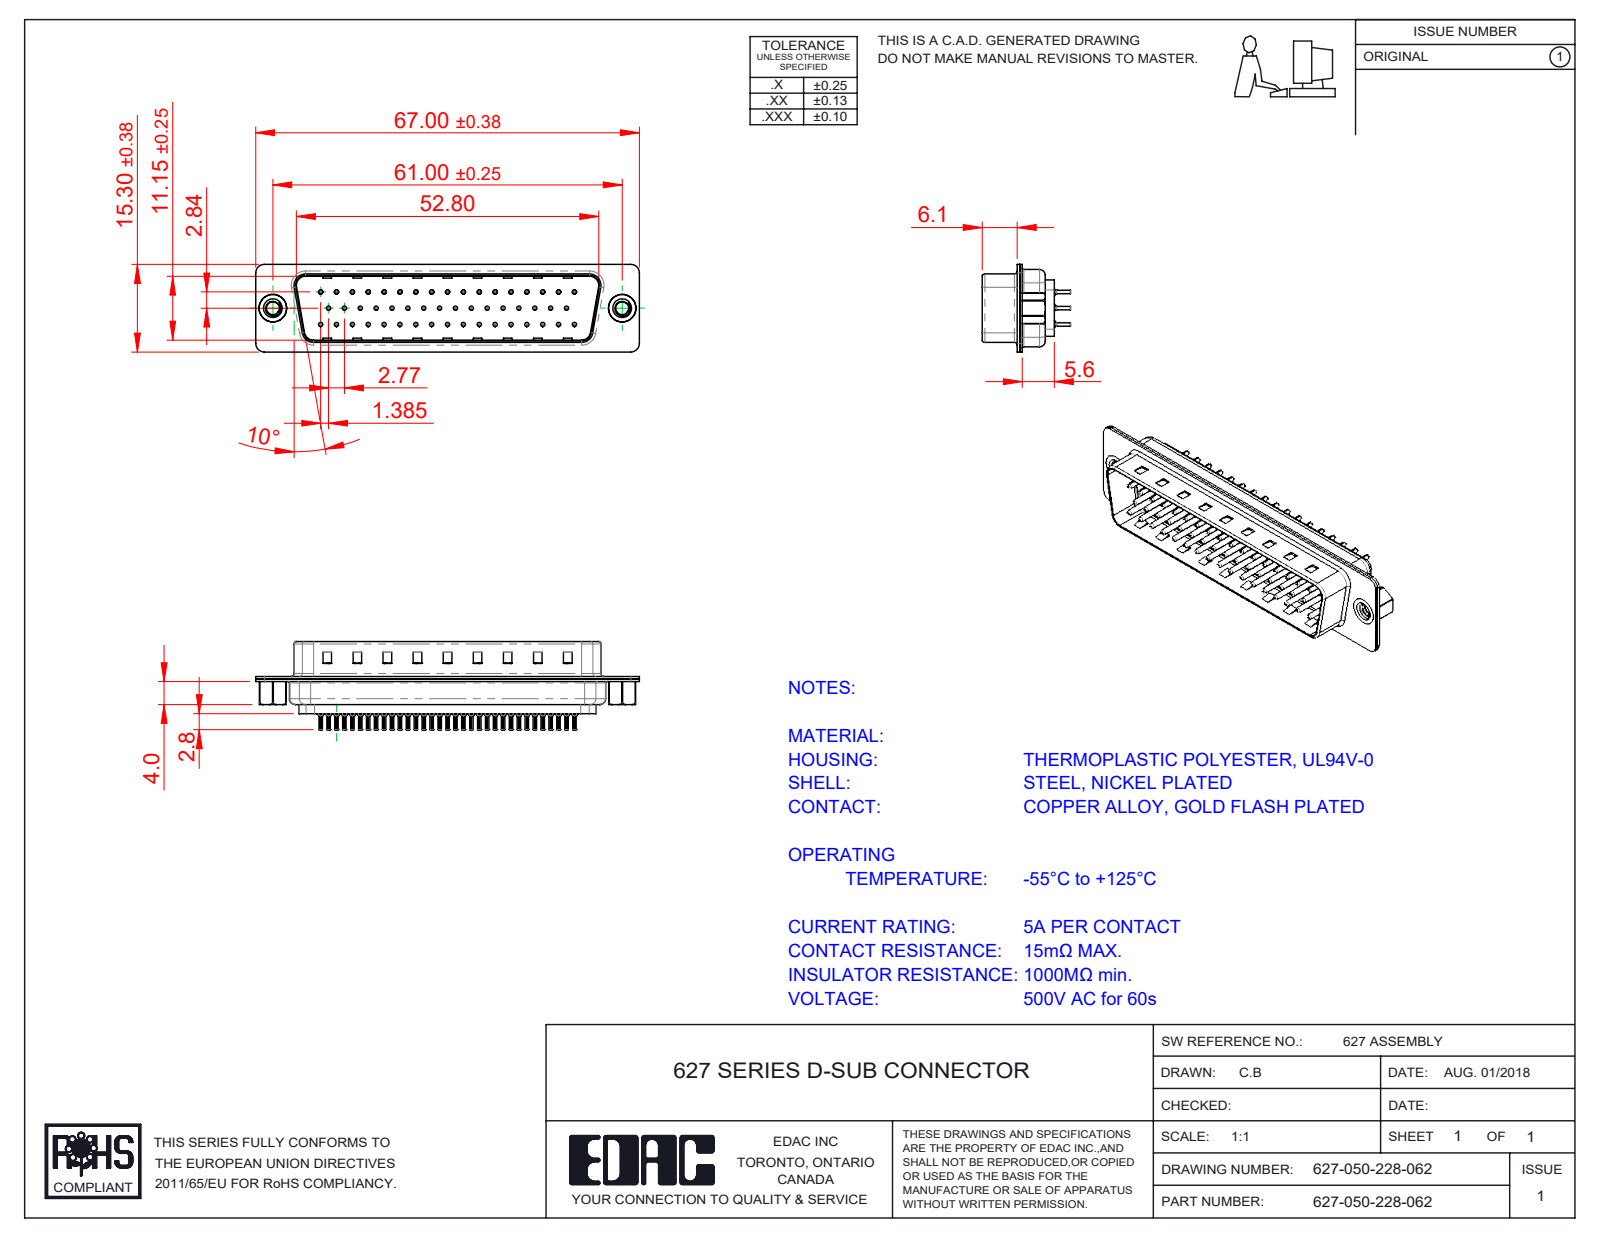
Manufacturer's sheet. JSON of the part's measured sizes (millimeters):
{"part_name": "627 Contact Row 1_28L; 627 Contact Row 3_28L; 627-050-228-062; 627 Contact Row 2_28L (+4 more)", "step_written_by": "SolidWorks 2020 (CONFIG_CONTROL_DESIGN)", "units": "millimeters", "bodies": {"solids": 56, "faces": 5419, "planar": 1409, "cylindrical": 2094, "other": 1916}, "overall_size": [67, 18.8, 15.3], "volume_mm3": 5550, "surface_area_mm2": 14620, "round_holes": [[0.2, 50], [0.35, 50], [1.1, 50], [1.6, 50], [2.26, 2], [4, 2], [4.8, 2]], "round_bosses_or_shafts": [[2, 50], [1.5, 50], [0.75, 50], [0.6, 50], [5, 2], [4.9, 2]], "partial_cylinders_radius": [[0.1, 100], [1.5, 16], [2, 12], [0.5, 8], [1.6, 8], [0.25, 4], [0.6, 4], [0.65, 4]], "face_to_face_distances": [0.4, 6.05, 0.45, 11.55, 0.9, 2.8, 8.85, 9.3, 6.5, 0.78], "hole_center_spacings": [2.77, 3.16, 5.54, 8.31, 11.08, 13.85, 16.62, 19.39]}
